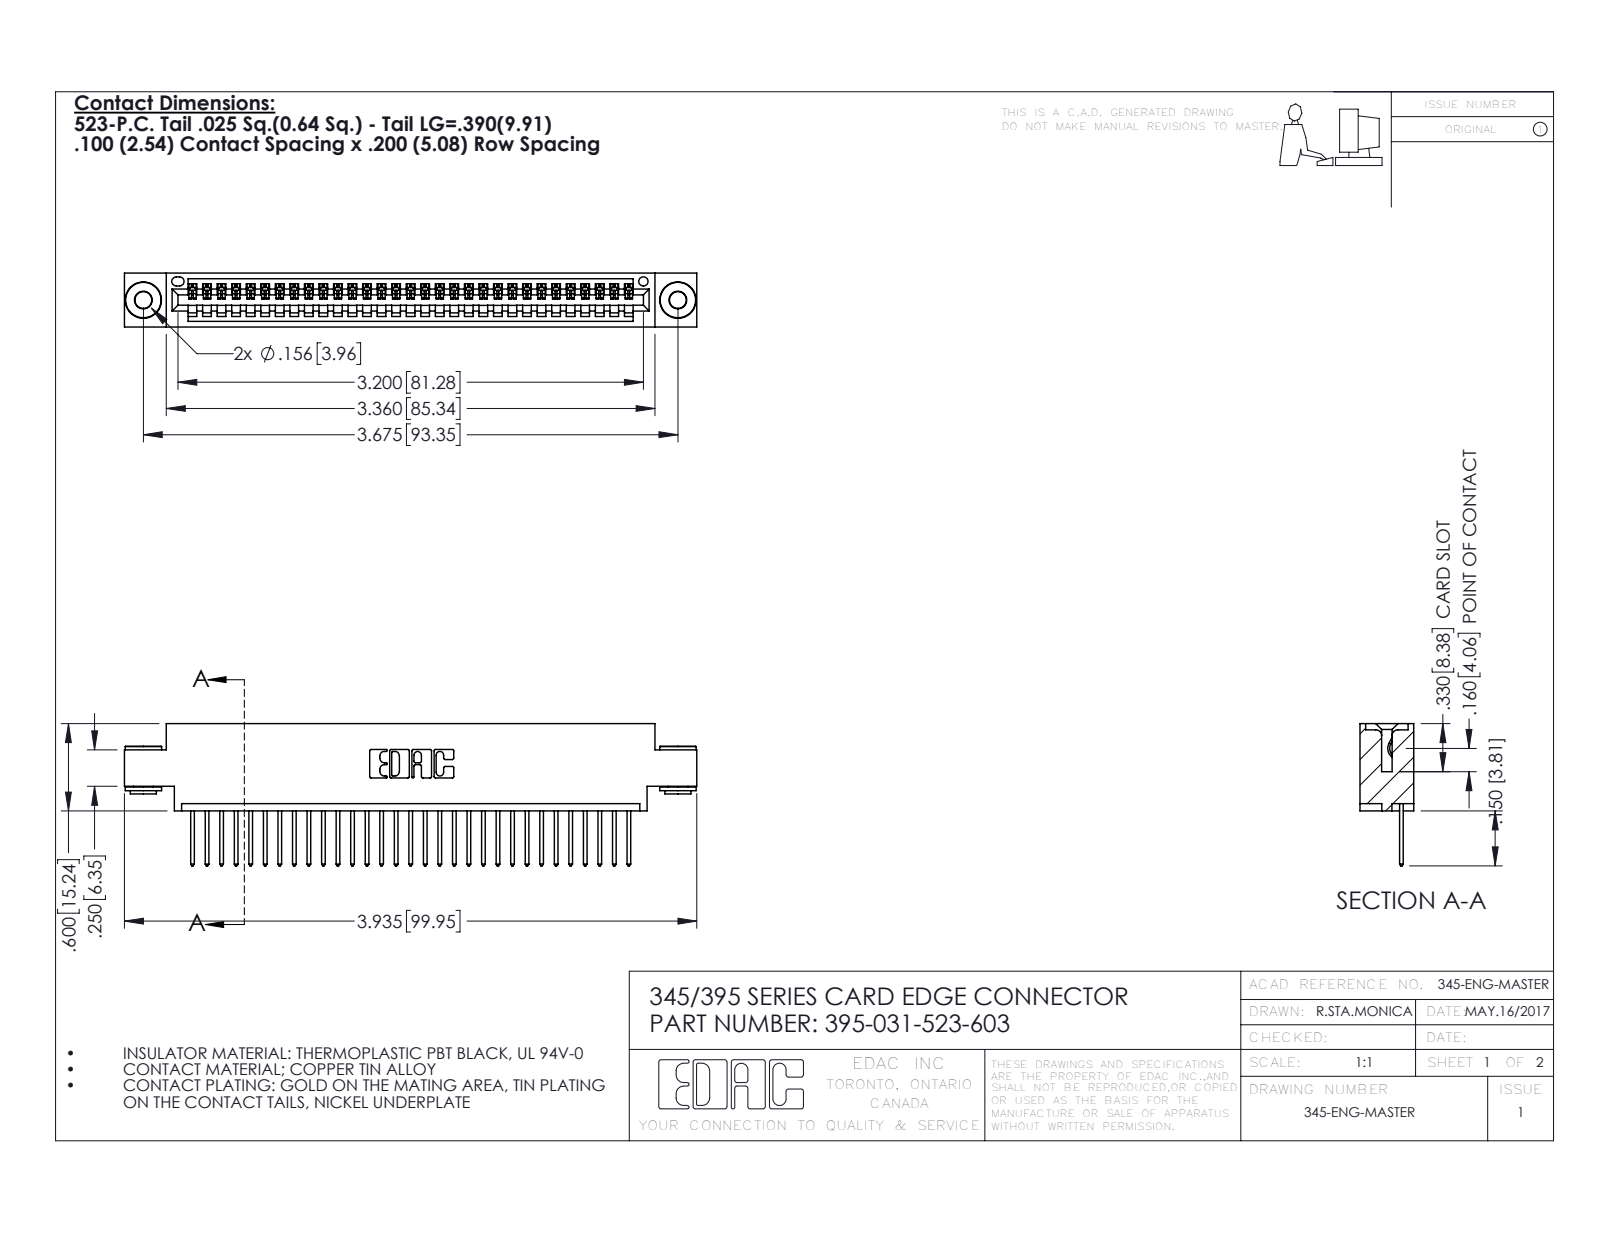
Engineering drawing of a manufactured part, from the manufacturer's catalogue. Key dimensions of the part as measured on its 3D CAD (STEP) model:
Part name (STEP PRODUCT): 345-250-002_345-250-002-102; 345-292-001_345-293-123; 395-031-523-603; 345 Part_0.170 Offset - 0.156 Dia-TH
STEP written by: SolidWorks 2016 (CONFIG_CONTROL_DESIGN)
Units: inches
Bodies: 34 solids, 1966 faces (1334 planar, 624 cylindrical, 8 other)
Overall size (bounding box): 3.935 × 0.977 × 0.37
Volume: 0.567 in³ · Surface area: 19.5 in²
Round holes (diameter × count): ⌀0.116 ×2, ⌀0.156 ×2, ⌀0.064 ×1
Round bosses / shafts (diameter × count): ⌀0.25 ×2, ⌀0.18 ×2, ⌀0.136 ×2
Partial cylindrical surfaces — rounded edges, fillets, slot ends (radius × count): R0.006 ×62, R0.01 ×62, R0.01 ×22, R0.007 ×6, R0.031 ×6, R0.026 ×3, R0.031 ×2, R0.04 ×2
Main face-to-face distances: 0.072, 0.298, 0.37, 0.2, 0.098, 0.272, 0.025, 0.225, 0.175, 0.149
Hole centre spacings: 0.27, 3.44, 3.675
